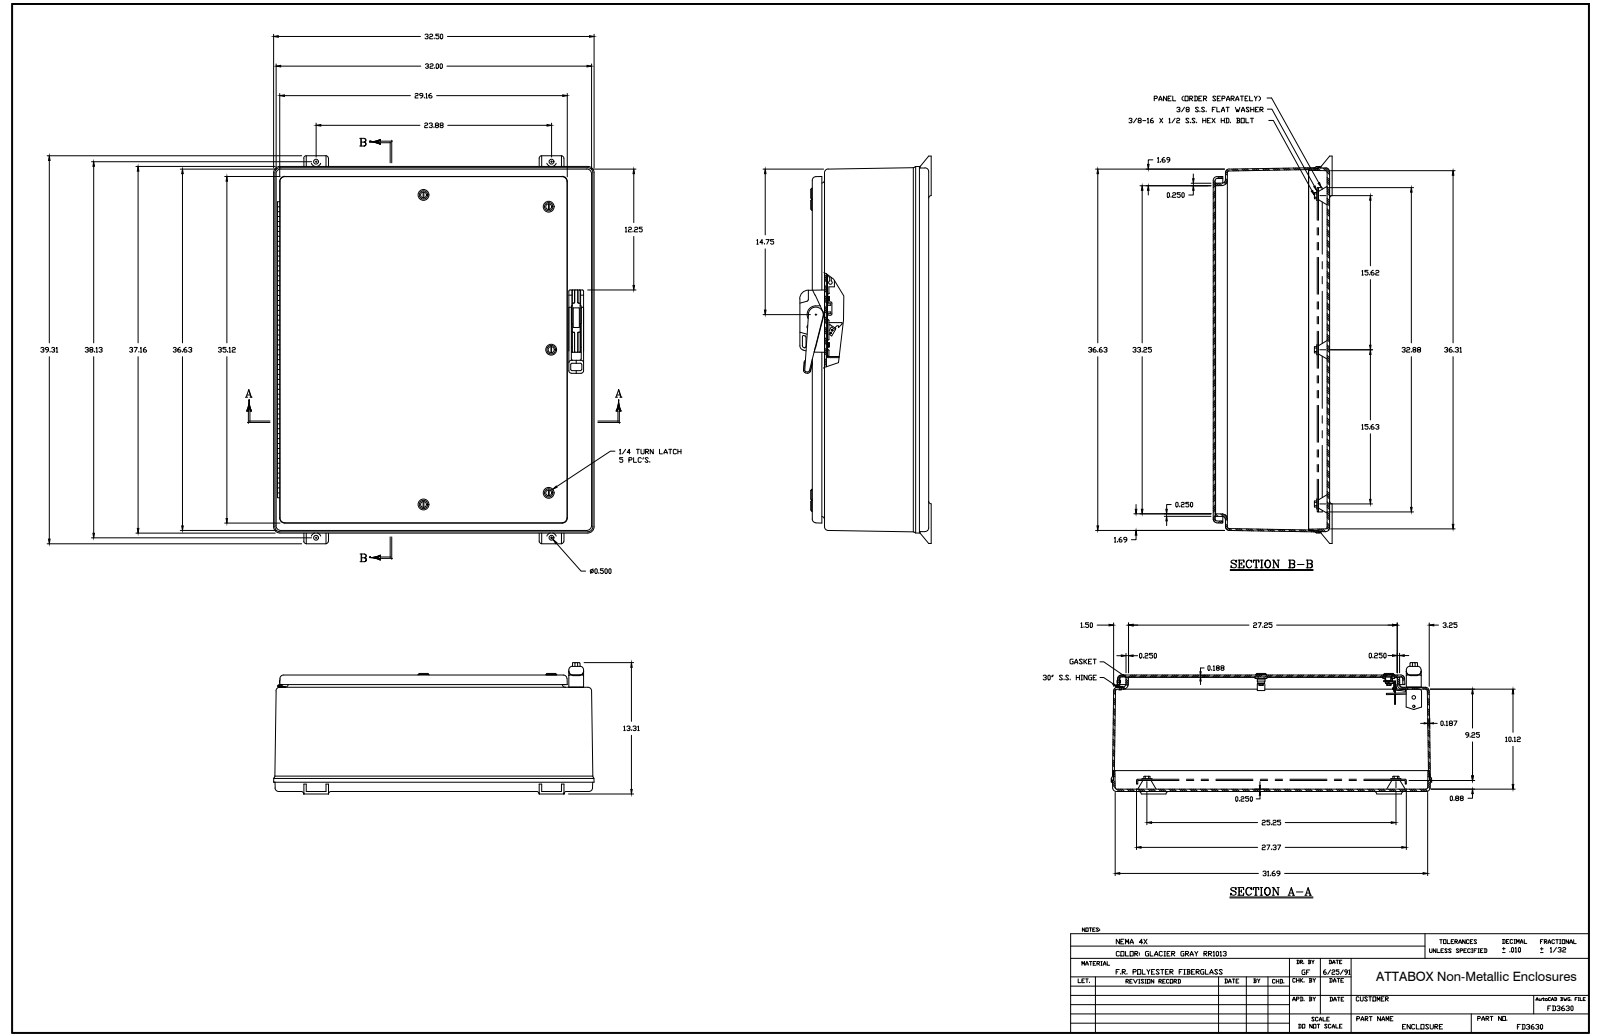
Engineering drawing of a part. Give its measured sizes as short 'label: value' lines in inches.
name: FD3630
written by: SolidWorks 2018 (AUTOMOTIVE_DESIGN)
unit: in
bodies: 99 solids, 3009 faces (1444 planar, 856 cylindrical, 709 other)
size: 39.31 × 32.5 × 13.313
volume: 1 021 in³; area: 10 907 in²
holes: 13× ⌀0.15, 10× ⌀0.5, 8× ⌀0.187, 6× ⌀0.257, 6× ⌀0.307, 6× ⌀0.433, 6× ⌀0.563, 5× ⌀0.63, 5× ⌀0.886, 4× ⌀0.171, 4× ⌀0.218, 4× ⌀0.281
bosses: 8× ⌀0.3, 7× ⌀0.2, 6× ⌀1, 6× ⌀0.374, 5× ⌀1.094, 5× ⌀0.63, 5× ⌀0.275, 4× ⌀0.357
rounds: 37× R0.25, 19× R0.125, 19× R0.156, 15× R0.188, 14× R0.313, 12× R0.5, 10× R0.187, 10× R0.375
face distances: 0.25, 0.187, 0.187, 11.81, 11.56, 11.622, 11.372, 0.13, 1.125, 0.875
hole spacings: 14.5, 9.185, 0.281, 6.451, 11.554, 18.37, 29, 0.014
